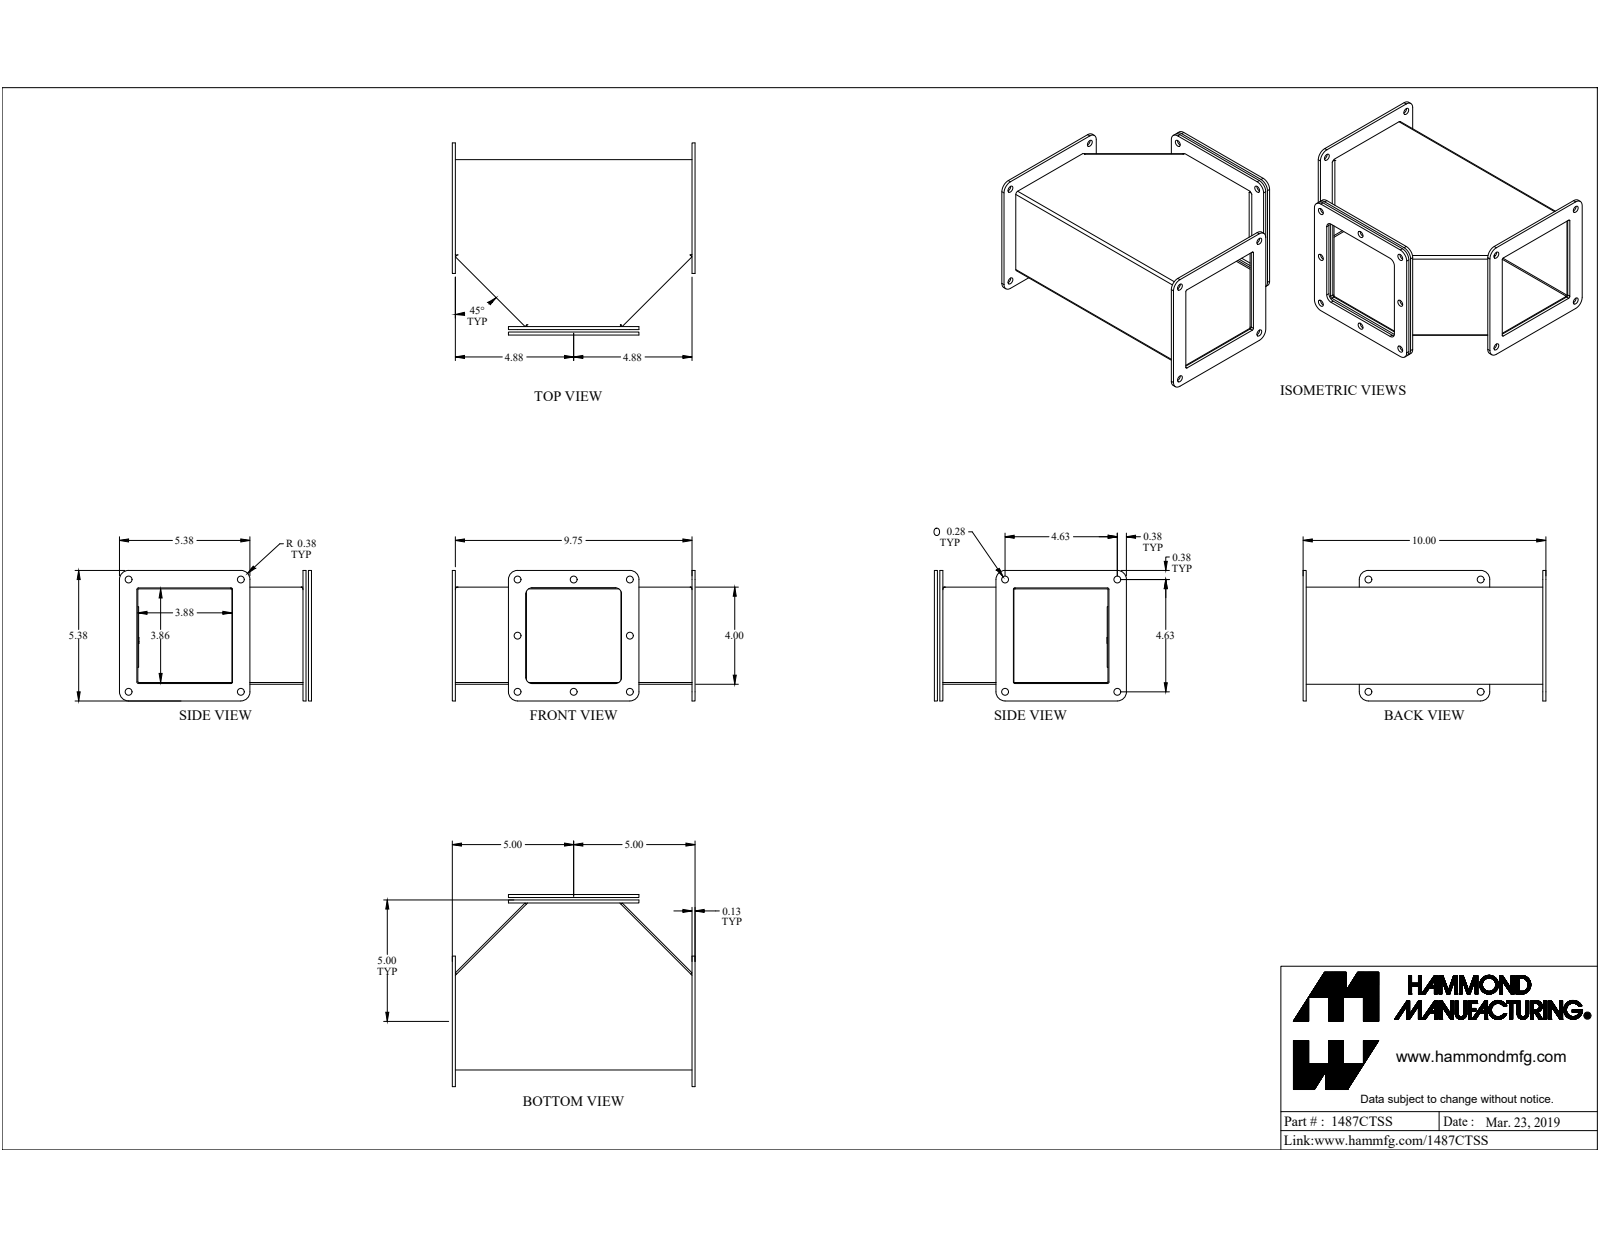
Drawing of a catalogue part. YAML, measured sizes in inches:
part_name: "1487CTSS"
step_written_by: "SolidWorks 2019 (CONFIG_CONTROL_DESIGN)"
units: inches
bodies: {solids: 9, faces: 300, planar: 187, cylindrical: 86, other: 27}
overall_size: [10, 8.258, 5.375]
volume: 20.2
surface_area: 520.9
round_holes:
  - {diameter: 0.281, count: 12}
  - {diameter: 0.196, count: 1}
  - {diameter: 0.258, count: 1}
  - {diameter: 0.35, count: 1}
round_bosses_or_shafts:
  - {diameter: 0.5, count: 1}
  - {diameter: 0.25, count: 1}
partial_cylinders:
  - {radius: 0.375, count: 12}
  - {radius: 0.062, count: 8}
  - {radius: 0.02, count: 6}
  - {radius: 0.036, count: 4}
  - {radius: 0.108, count: 4}
  - {radius: 0.25, count: 4}
face_to_face_distances: [0.072, 3.928, 4, 3.856, 0.125, 9.875, 9.75, 0.225, 0.125, 6.875]
hole_center_spacings: [2.313, 4.625, 5.171, 3.27, 4.625, 6.541, 6.541]
